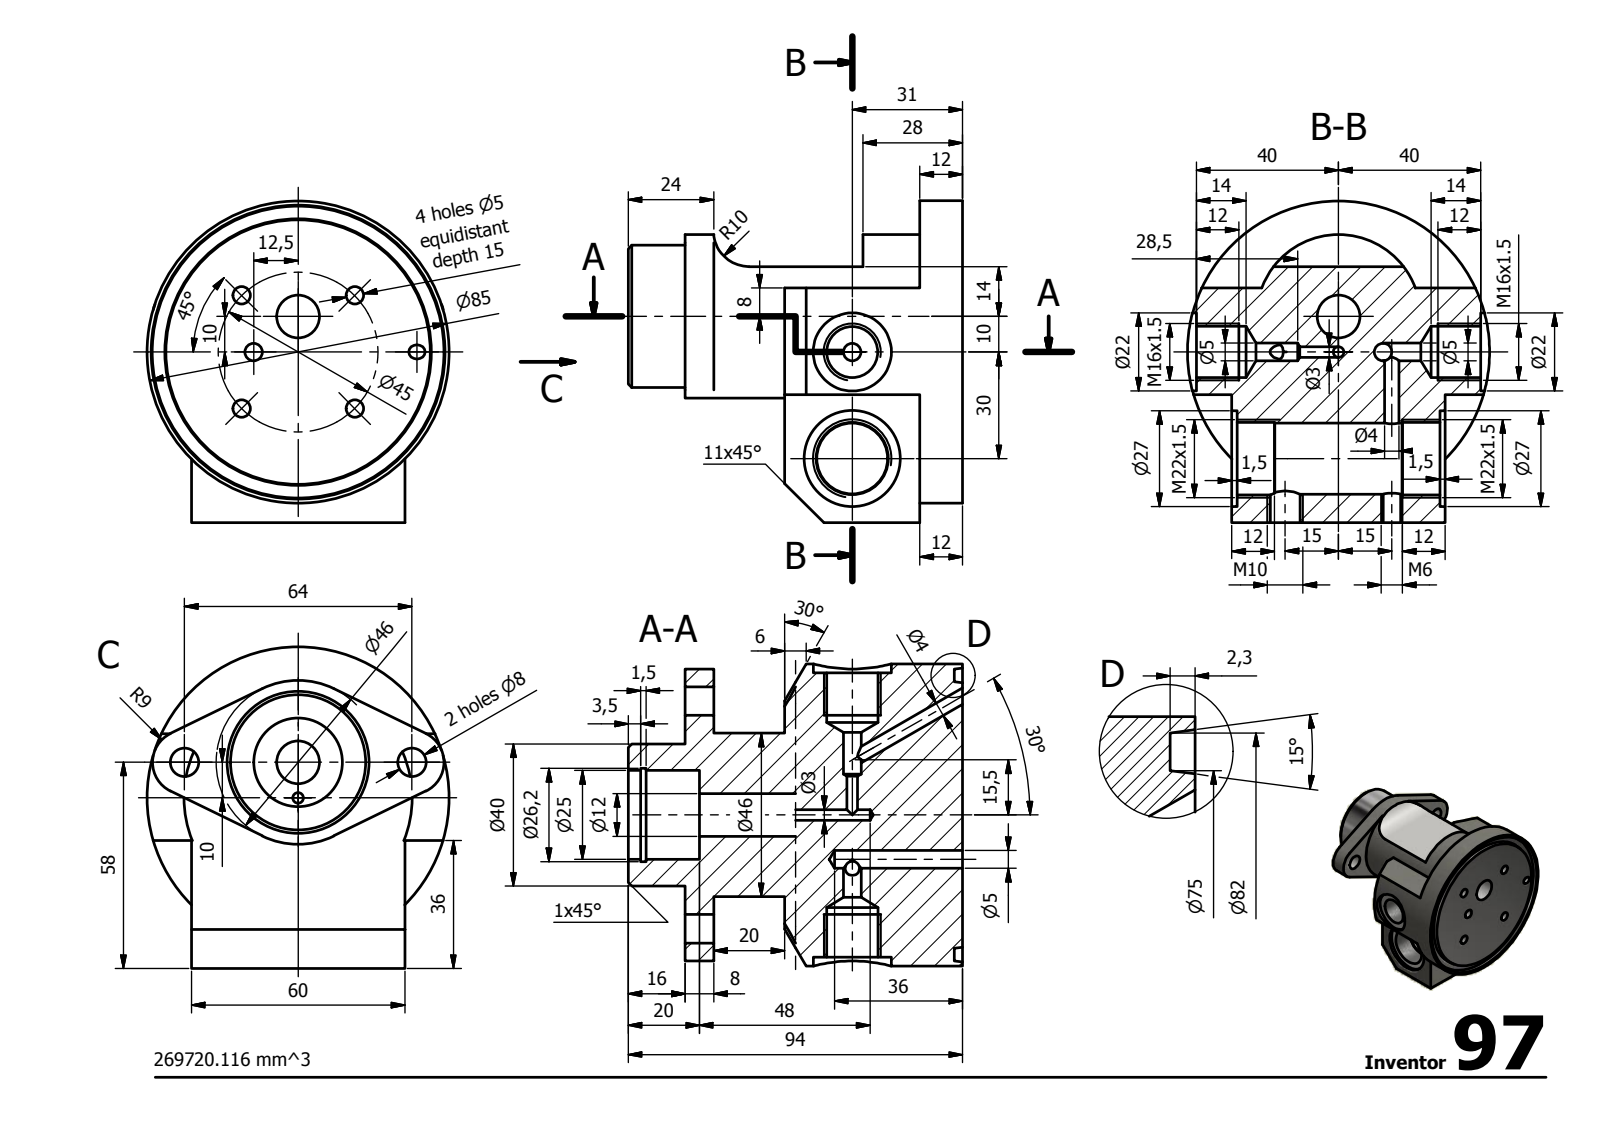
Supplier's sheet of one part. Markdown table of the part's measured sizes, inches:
| quantity | value |
| --- | --- |
| STEP written by | Autodesk Inventor 2014 (AUTOMOTIVE_DESIGN) |
| units | inches |
| bodies | 1 solid, 89 faces (35 planar, 36 cylindrical, 18 other) |
| overall size | 3.701 × 3.563 × 3.346 |
| volume | 16.46 in³ |
| surface area | 74.22 in² |
| round holes (diameter × count) | 0.197 × 6, 0.118 × 2, 0.157 × 2, 0.315 × 2, 0.194 × 1, 0.33 × 1, 0.472 × 1, 0.566 × 1, 0.787 × 1, 0.802 × 1, 0.866 × 1, 0.984 × 1 |
| round bosses / shafts (diameter × count) | 3.346 × 1, 1.811 × 1, 1.575 × 1 |
| partial cylindrical surfaces (radius × count) | 0.354 × 2, 0.394 × 1 |
| main face-to-face distances | 2.598, 1.969, 1.496, 0.472, 1.417, 1.102, 2.756, 2.835, 0.236, 3.071 |
| hole center spacings | 0.886, 1.253, 0.641, 0.668, 0.675, 1.181, 1.197, 1.201 |
